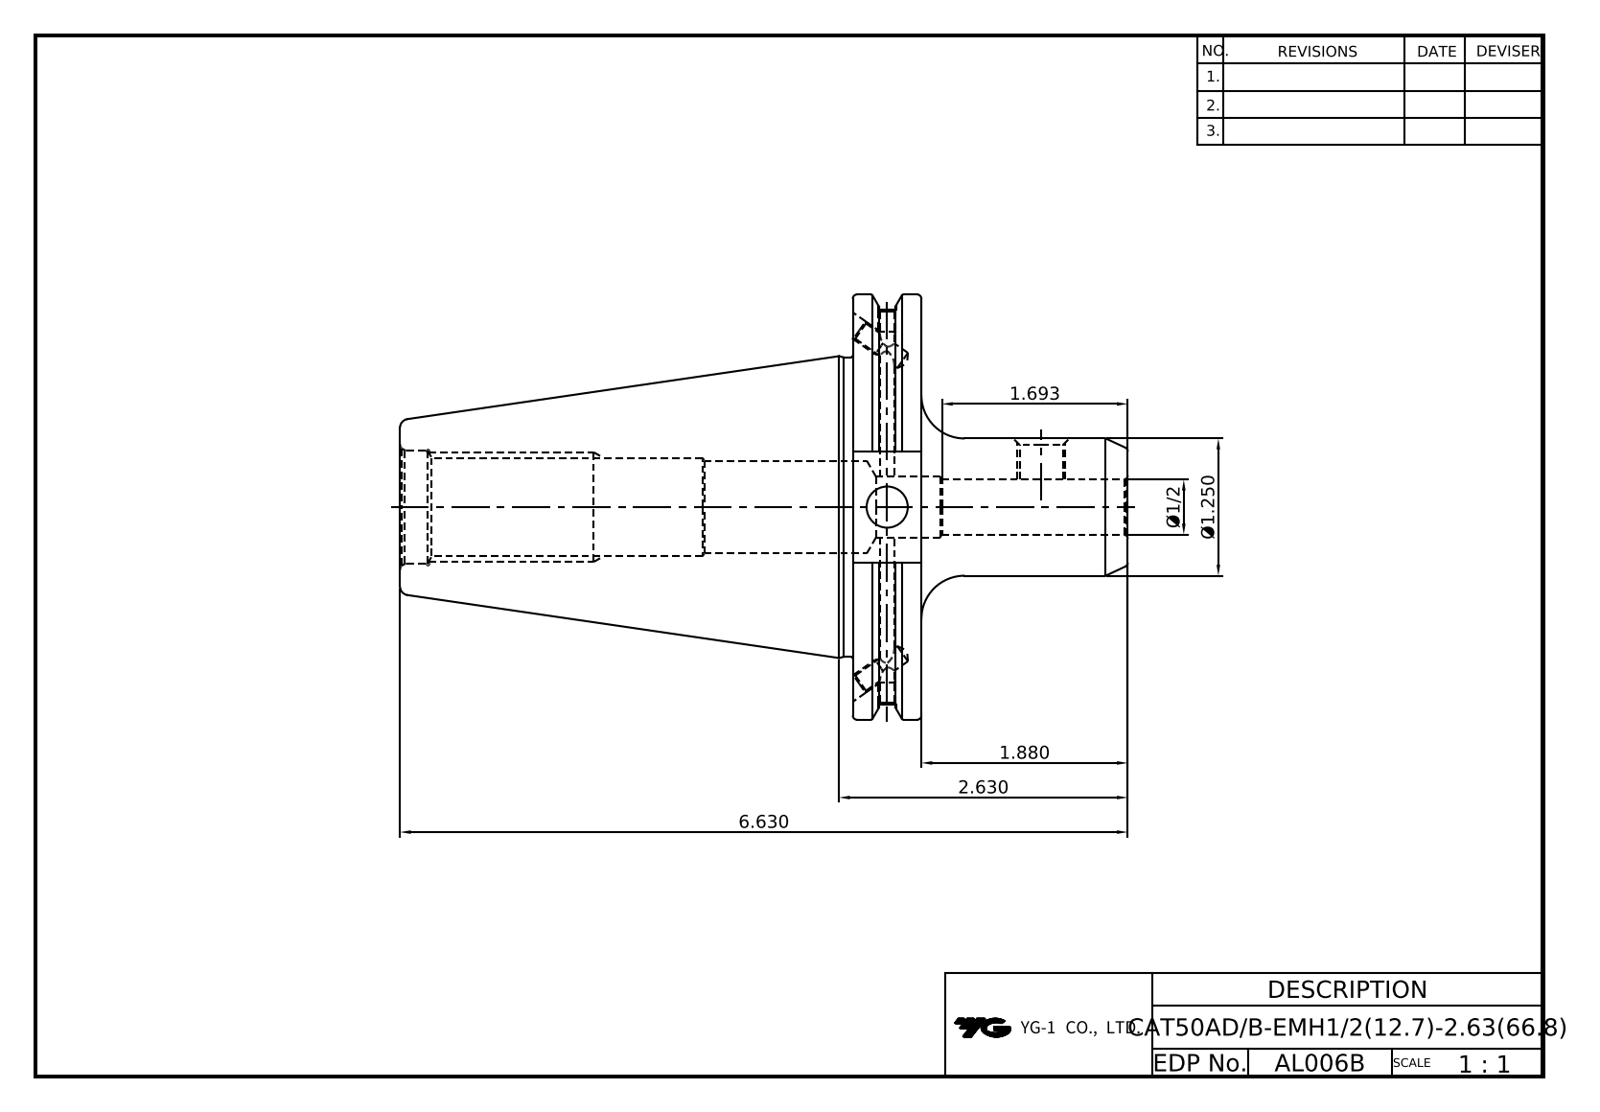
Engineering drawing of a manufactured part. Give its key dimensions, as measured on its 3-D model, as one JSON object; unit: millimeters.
{"part_name": "CAT50ADB-EMH12.7-66.8", "step_written_by": "Autodesk Inventor 2020 (AUTOMOTIVE_DESIGN)", "units": "millimeters", "bodies": {"solids": 1, "faces": 89, "planar": 36, "cylindrical": 27, "other": 26}, "overall_size": [168.4, 98.42, 94.69], "volume_mm3": 352497, "surface_area_mm2": 51459, "round_holes": [[3.24, 2], [4.13, 2], [4.2, 2], [5, 2], [9.53, 1], [9.73, 1], [12.7, 1], [14, 1], [21.5, 1], [21.97, 1], [26.2, 1]], "round_bosses_or_shafts": [[98.42, 1], [91.29, 1], [69.25, 1], [31.75, 1]], "face_to_face_distances": [15.88, 104.77, 120.65, 168.4, 63.63, 47.75, 73.03, 25.9, 110.82, 6.05]}
